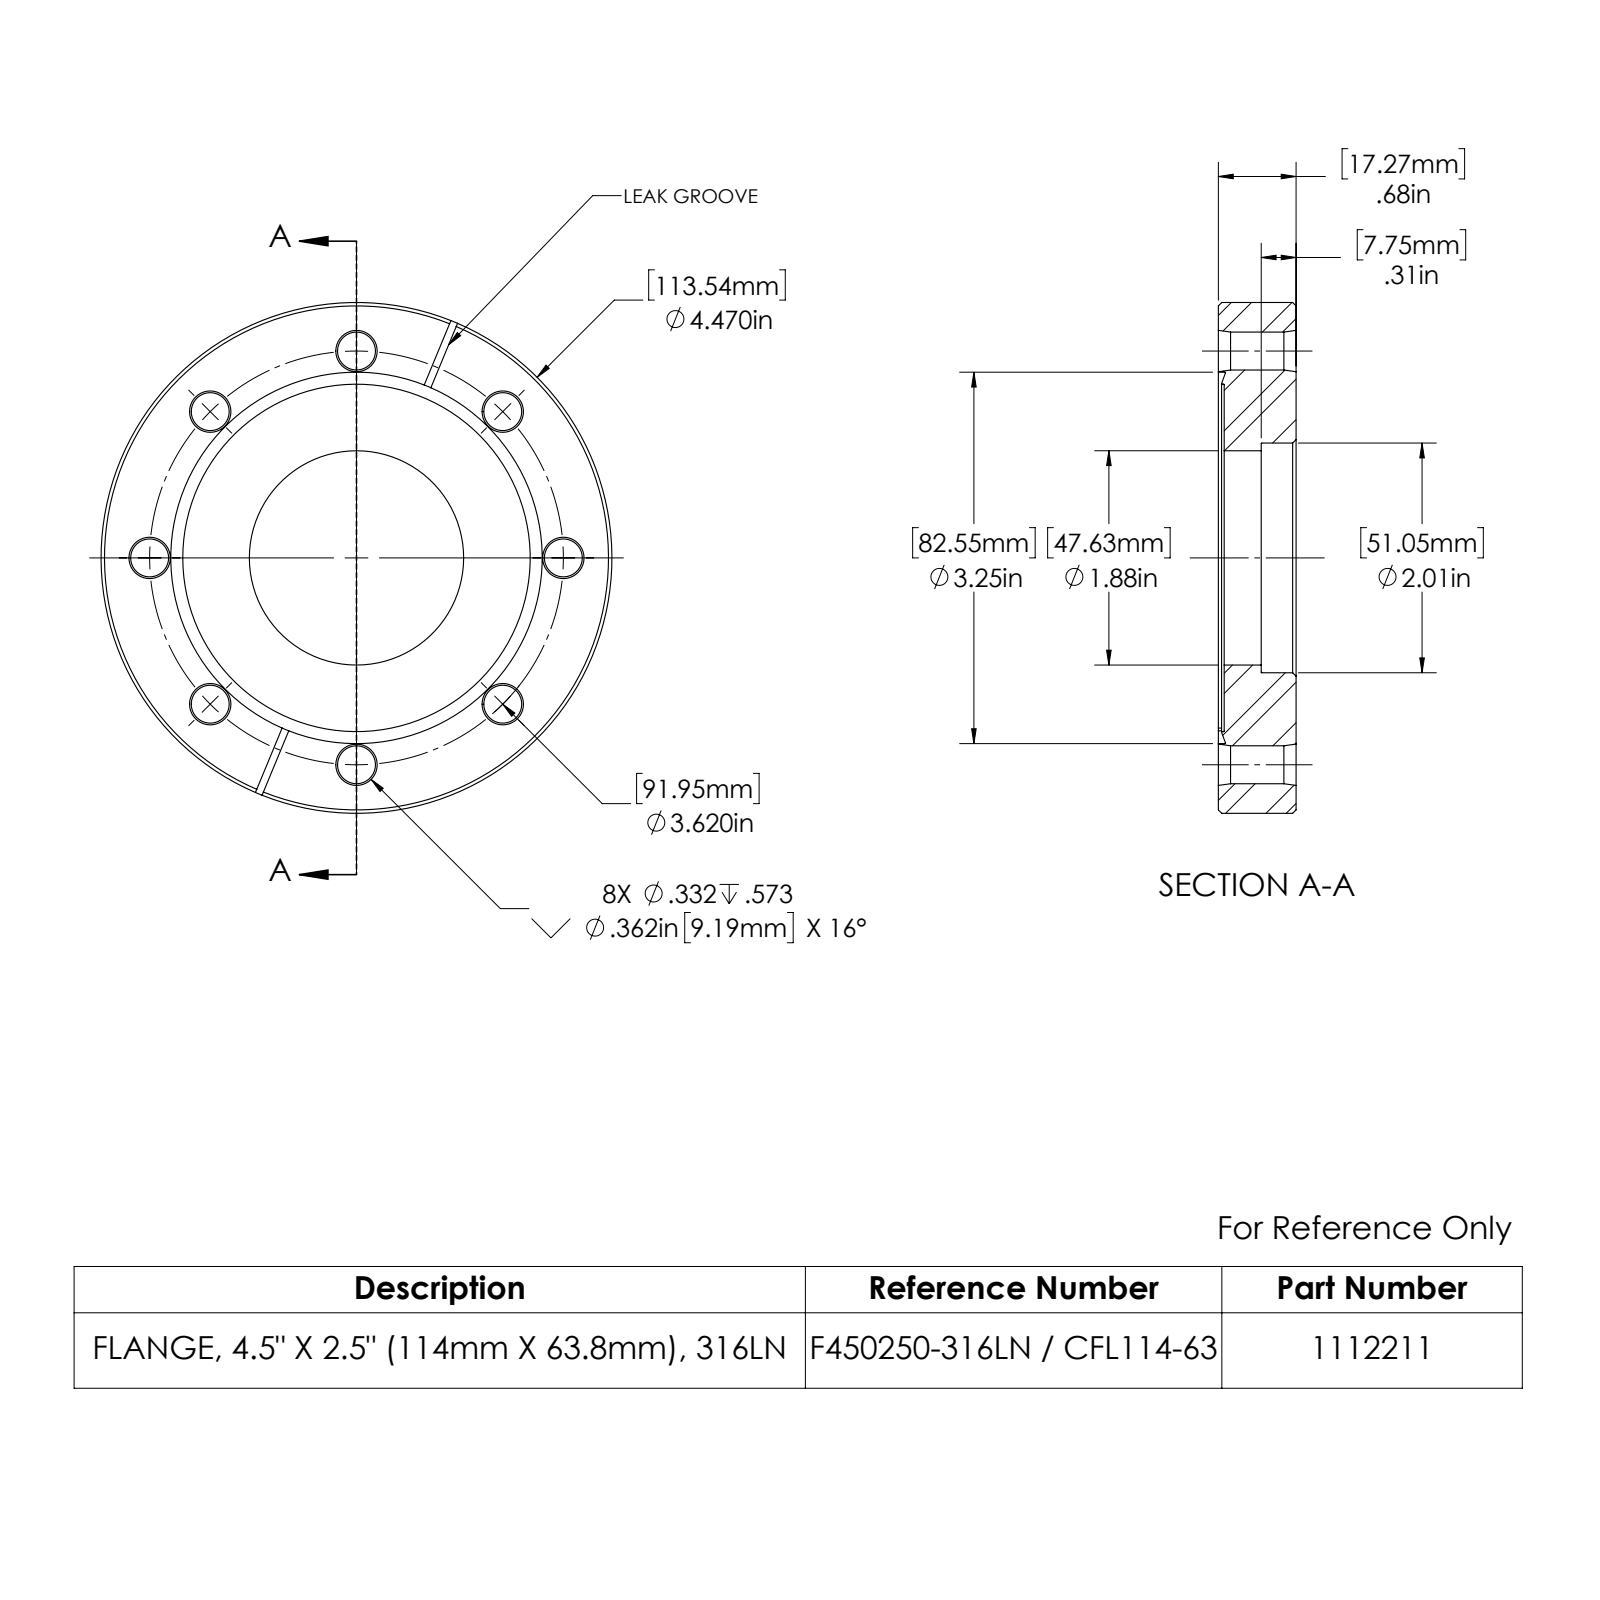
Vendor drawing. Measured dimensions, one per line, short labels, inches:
name: 1112211
written by: SolidWorks 2022 (AUTOMOTIVE_DESIGN)
unit: in
bodies: 1 solid, 86 faces (11 planar, 26 cylindrical, 49 other)
size: 4.47 × 4.47 × 0.68
volume: 7.888 in³; area: 43.71 in²
holes: 8× ⌀0.332, 1× ⌀1.875, 1× ⌀2.01, 1× ⌀3.04, 1× ⌀3.25
bosses: 1× ⌀4.47
face distances: 0.68, 0.051, 0.629, 0.375, 0.324, 0.305, 0.05, 0.325, 0.63, 0.063
hole spacings: 1.385, 3.344, 1.81, 1.81, 2.559, 2.56, 3.62, 3.62
